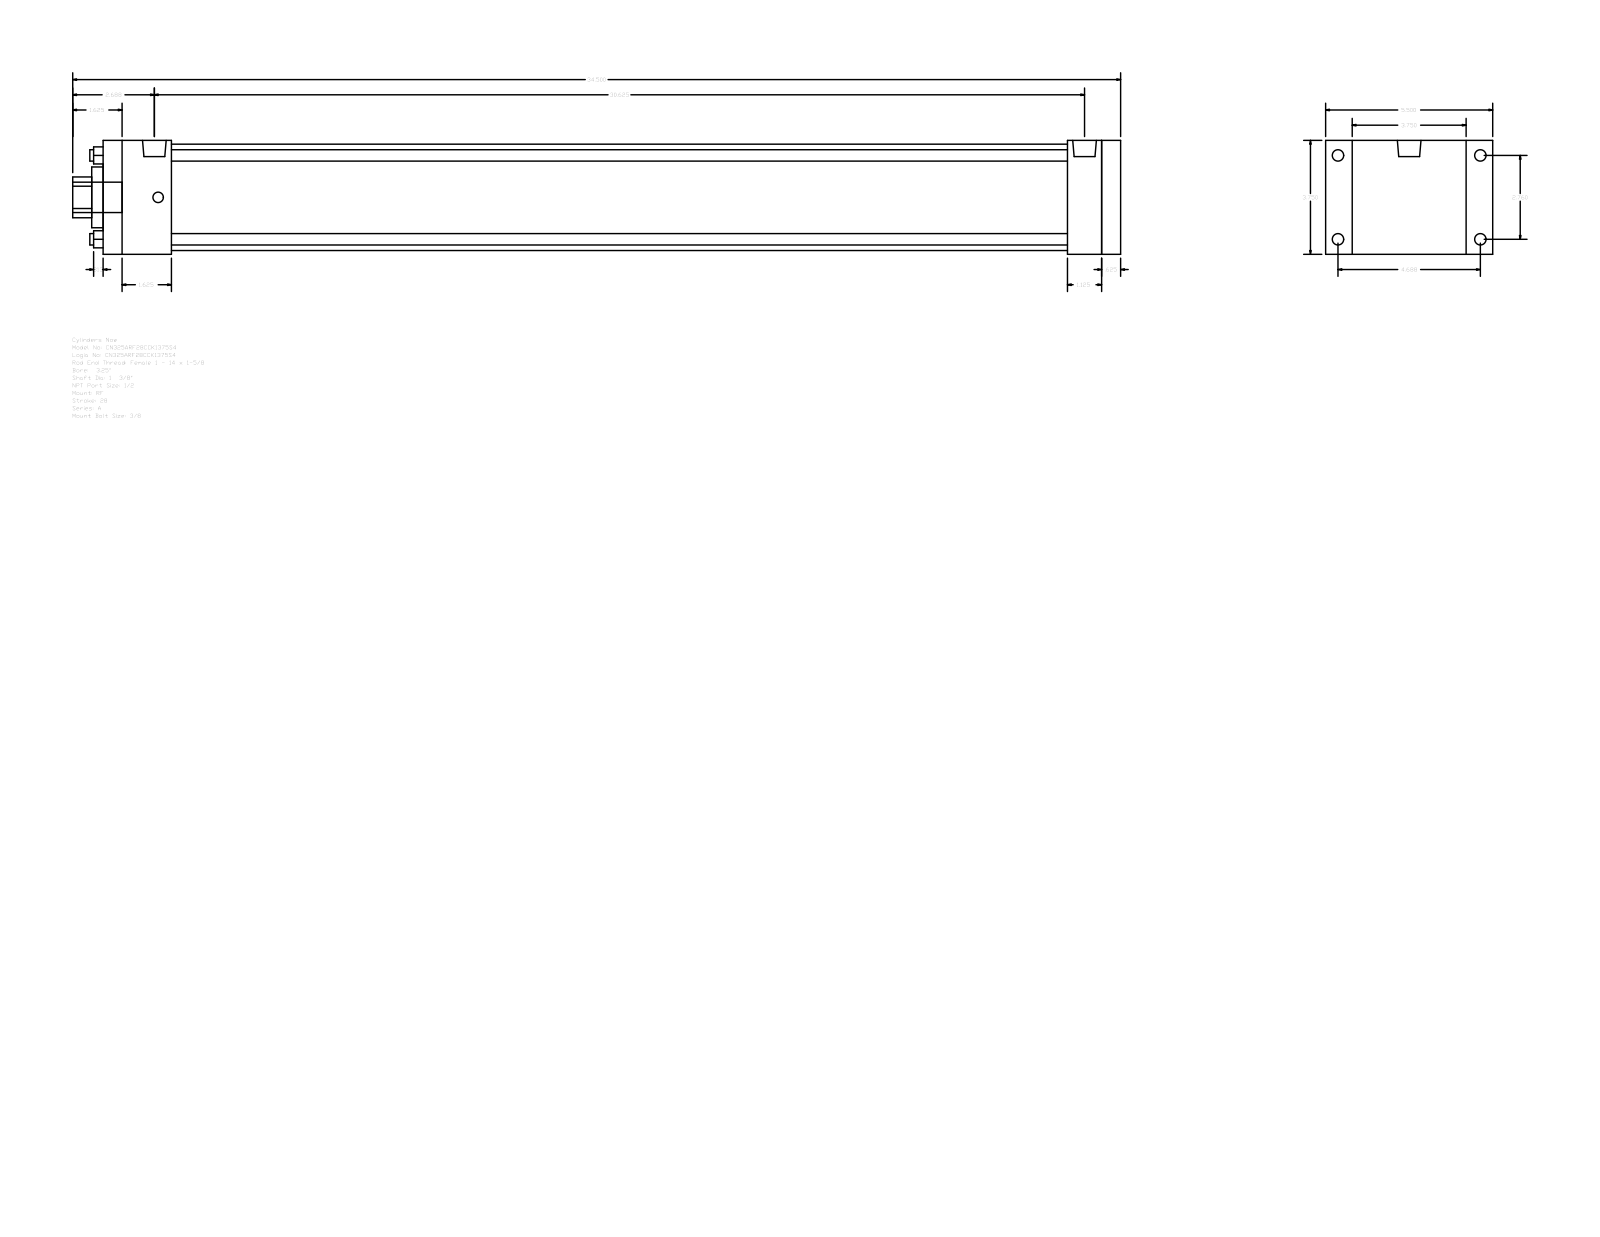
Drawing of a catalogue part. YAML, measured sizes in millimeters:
part_name: "A_RF__0325_1.375"
step_written_by: "GSSL Pune (CONFIG_CONTROL_DESIGN)"
units: millimeters
bodies: {solids: 0, faces: 92, planar: 64, cylindrical: 28, other: 0}
overall_size: [876.3, 139.7, 95.25]
round_holes:
  - {diameter: 9.53, count: 4}
  - {diameter: 34.92, count: 1}
  - {diameter: 50.8, count: 1}
  - {diameter: 88.9, count: 1}
round_bosses_or_shafts:
  - {diameter: 9.53, count: 4}
  - {diameter: 8.73, count: 4}
  - {diameter: 19.77, count: 2}
  - {diameter: 25.4, count: 1}
partial_cylinders:
  - {radius: 17.06, count: 1}
face_to_face_distances: [95.24, 850.9, 15.88, 835.02, 22.23, 117.47, 28.57, 806.45, 44.45, 57.15]
hole_center_spacings: [49.57, 70.1, 99.14]
